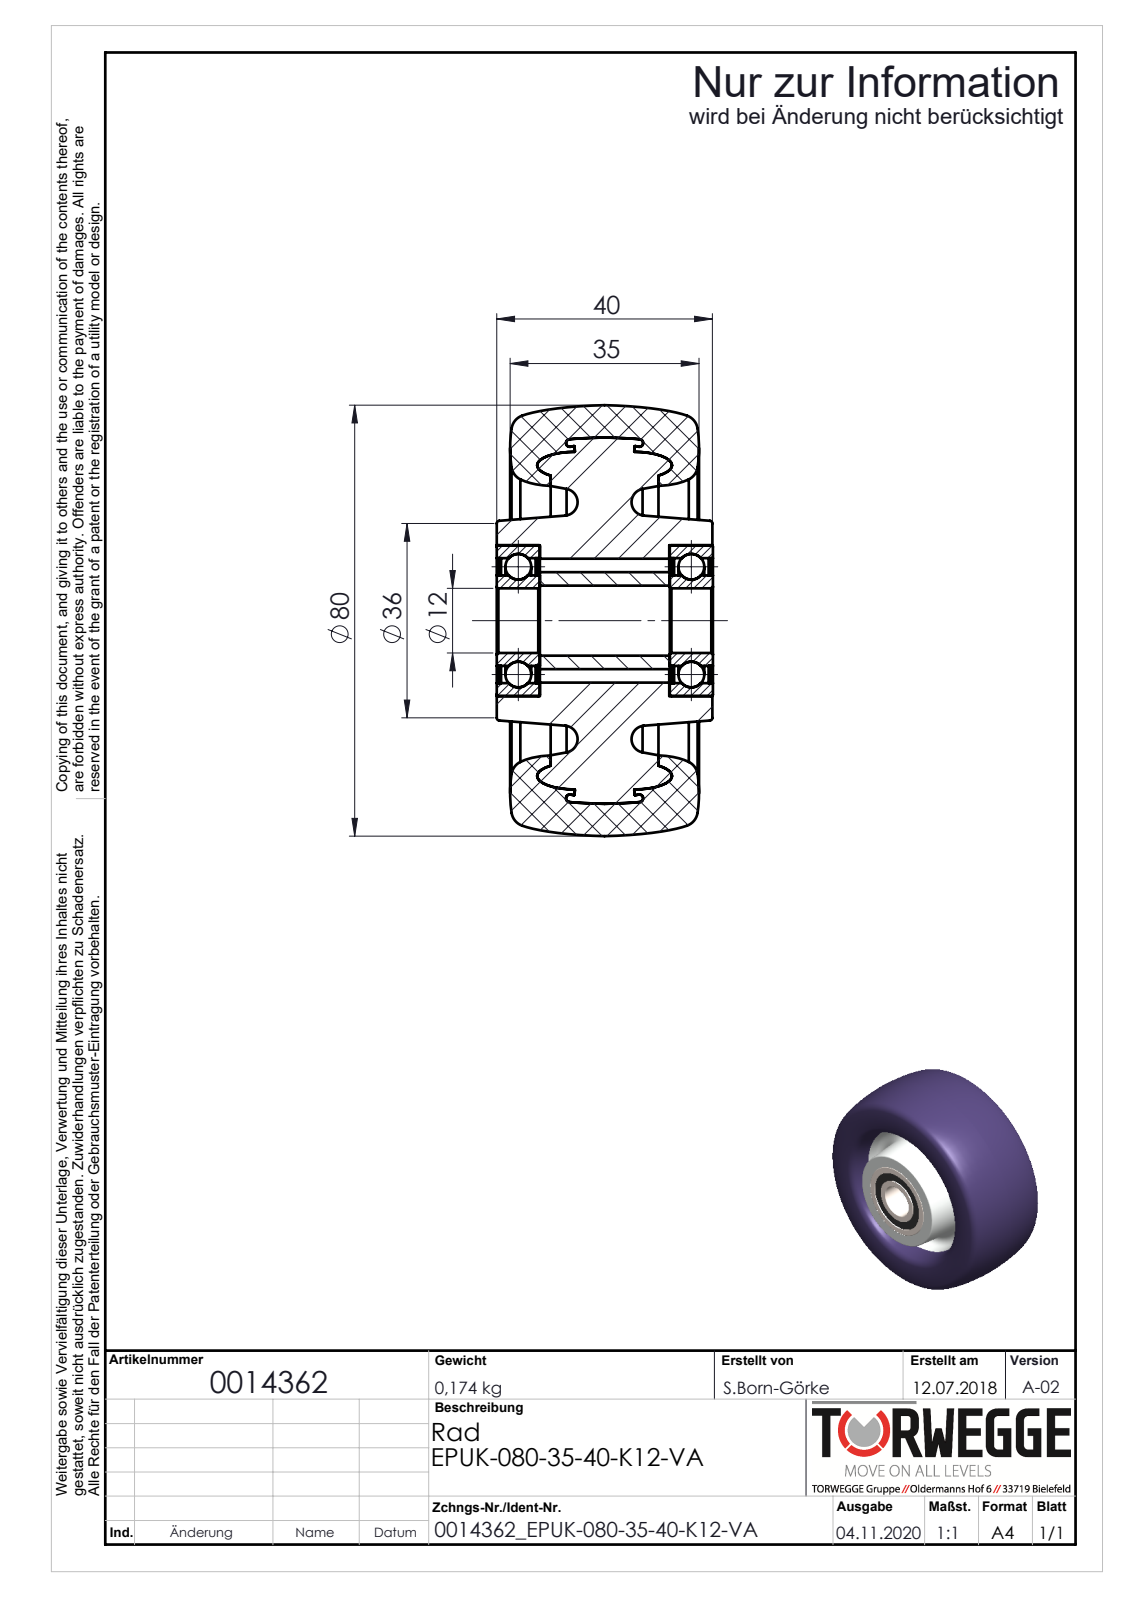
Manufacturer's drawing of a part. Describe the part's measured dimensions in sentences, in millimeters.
The part is named "0014362". Its 3-D file was written by "SolidWorks 2018 (AUTOMOTIVE_DESIGN)". It is 12 solids with 249 faces: 36 planar, 57 cylindrical and 156 other. Overall it measures 80 by 80 by 40.1 millimeters. Its volume is 141 433 cubic millimeters and its surface area 38 395 square millimeters. Round holes: 1 of diameter 12, 1 of diameter 13, 1 of diameter 16.8, 1 of diameter 23, 1 of diameter 23.2, 1 of diameter 28. Round bosses or shafts: 1 of diameter 18. Partial cylindrical surfaces (rounded edges, fillets, slot ends): 1 of radius 31.4. The main face-to-face distances are 32.1, 8, 0.8, 7.2, 7.7, 0.5, 6.9, 32, 40, 32.4.
